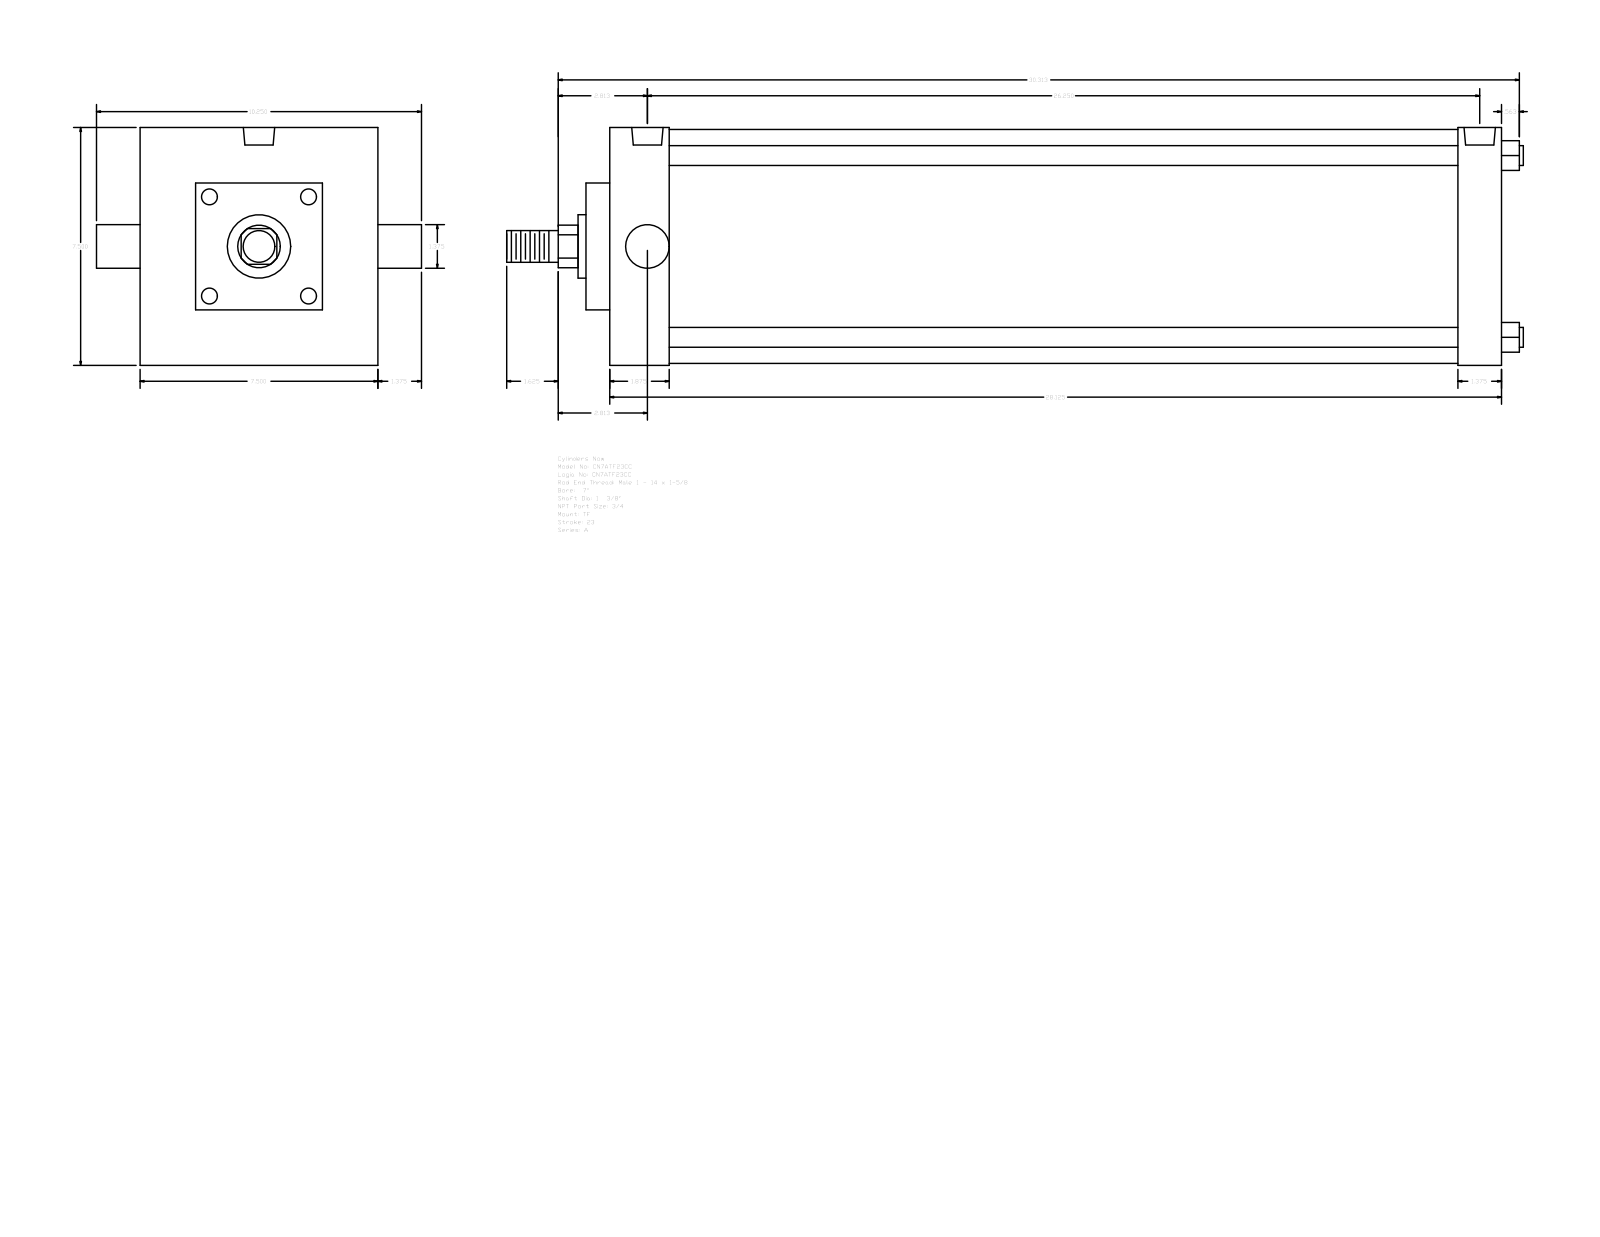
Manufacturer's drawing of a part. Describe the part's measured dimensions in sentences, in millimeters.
The part is named "A_TF__0700_1.375". Its 3-D file was written by "GSSL Pune (CONFIG_CONTROL_DESIGN)". It is 0 solids with 89 faces: 65 planar, 24 cylindrical and 0 other. Overall it measures 814.39 by 260.35 by 190.5 millimeters. Round holes: 3 of diameter 15.08, 2 of diameter 25.12. Round bosses or shafts: 4 of diameter 15.88, 2 of diameter 34.92, 1 of diameter 187.32, 1 of diameter 50.8, 1 of diameter 25.4. Partial cylindrical surfaces (rounded edges, fillets, slot ends): 1 of radius 17.06. The main face-to-face distances are 190.5, 714.38, 19.04, 733.42, 66.67, 47.63, 666.75, 698.5, 679.46, 631.83. The hole center spacings are 5.56, 661.19, 655.63, 666.75.
